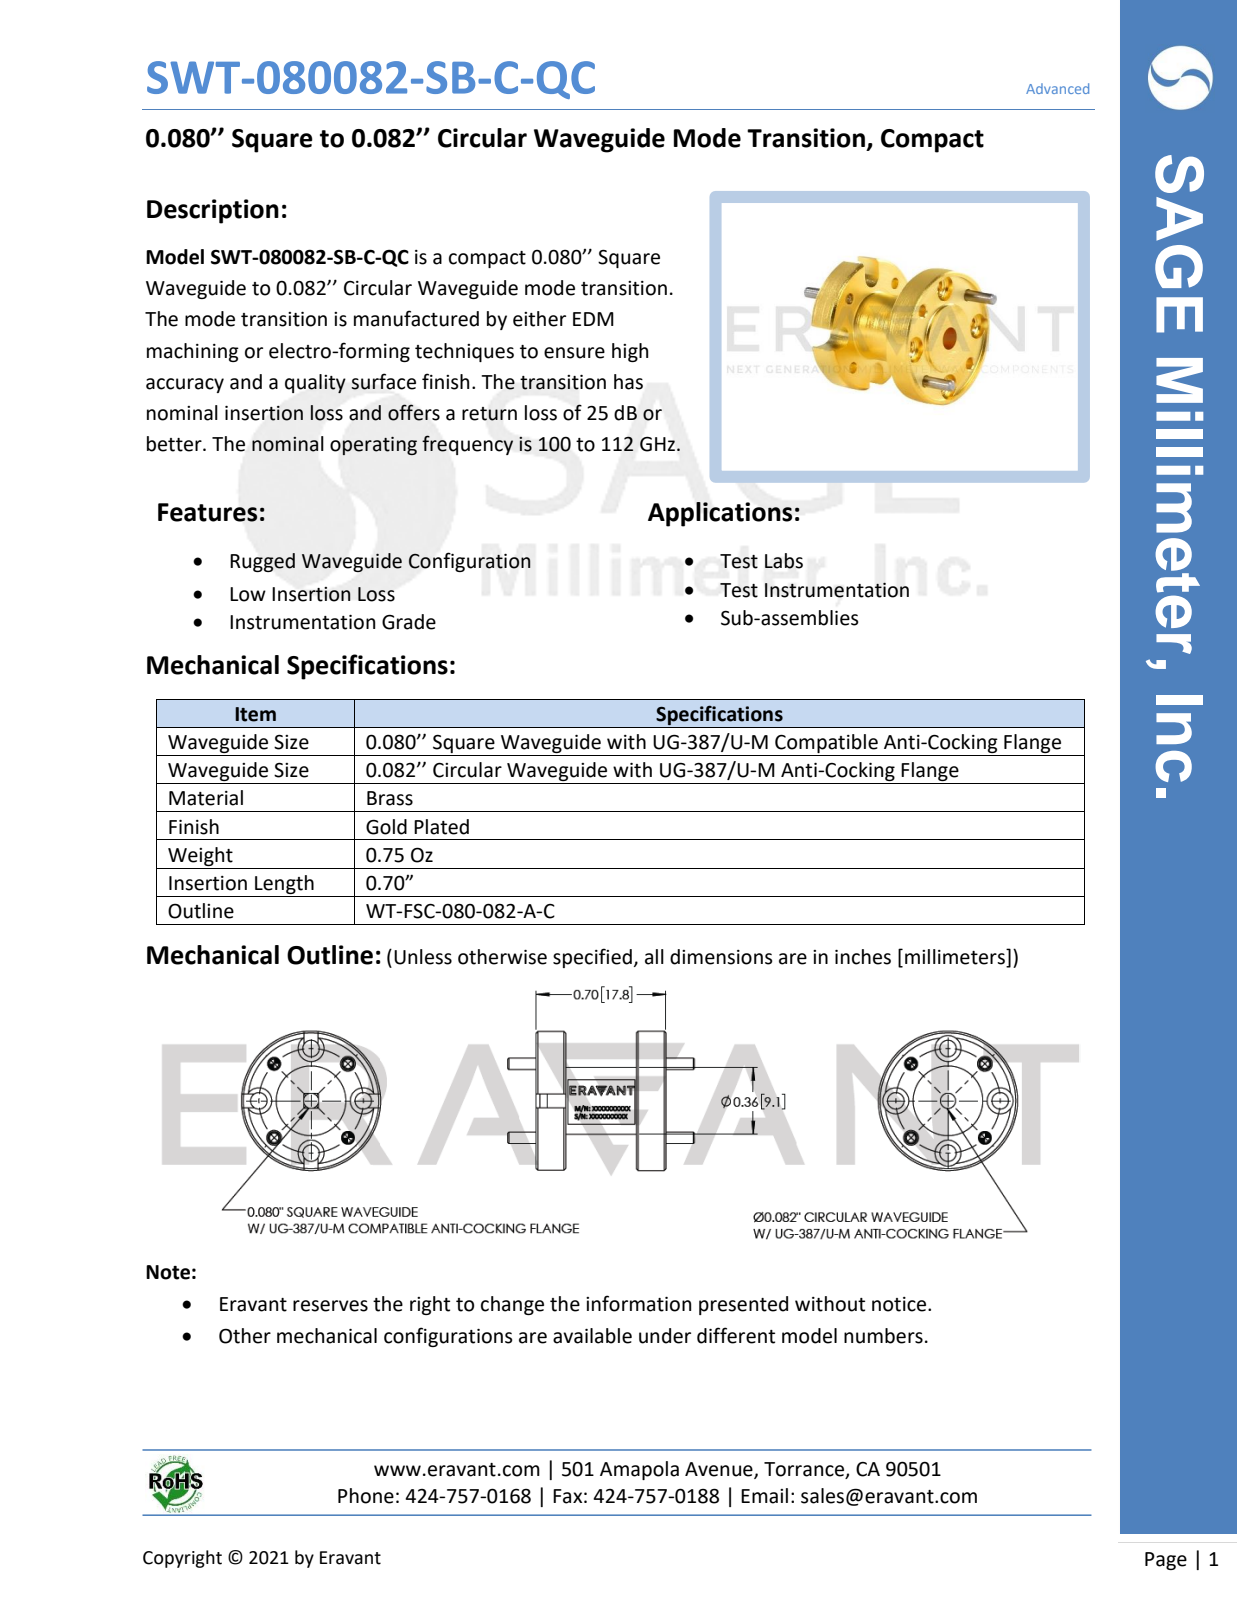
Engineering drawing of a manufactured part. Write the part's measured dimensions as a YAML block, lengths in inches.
part_name: "WT-FSC-080-082-A-C"
step_written_by: "SolidWorks 2021 (AUTOMOTIVE_DESIGN)"
units: inches
bodies: {solids: 5, faces: 175, planar: 45, cylindrical: 78, other: 52}
overall_size: [1.005, 0.75, 0.75]
volume: 0.157
surface_area: 3.445
round_holes:
  - {diameter: 0.061, count: 4}
  - {diameter: 0.067, count: 4}
  - {diameter: 0.089, count: 4}
  - {diameter: 0.14, count: 4}
  - {diameter: 0.68, count: 1}
round_bosses_or_shafts:
  - {diameter: 0.063, count: 4}
  - {diameter: 0.75, count: 1}
  - {diameter: 0.375, count: 1}
  - {diameter: 0.36, count: 1}
face_to_face_distances: [0.14, 0.52, 0.02, 0.16, 0.54, 0.68, 0.38, 0.66, 0.7, 0.06]
hole_center_spacings: [0.215, 0.281, 0.398, 0.519, 0.562]
